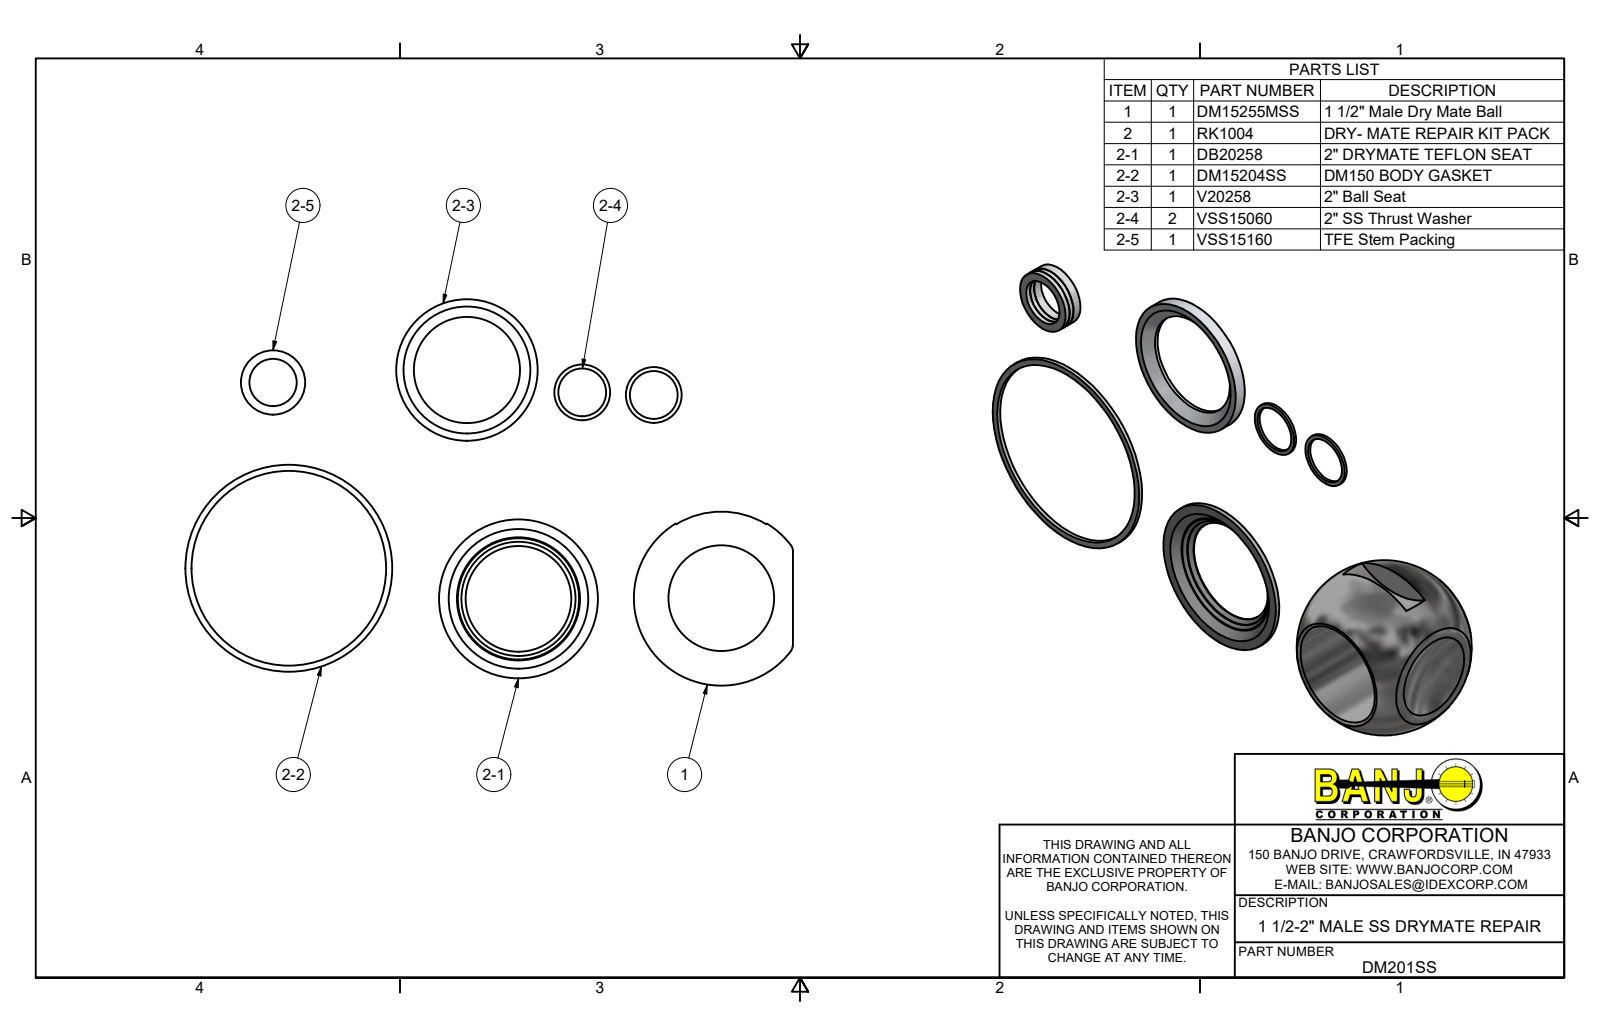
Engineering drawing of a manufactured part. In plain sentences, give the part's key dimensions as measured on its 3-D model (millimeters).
The part is named "DM201SS; RK1004; DB20258; DM15204SS (+7 more)". Its 3-D file was written by "Autodesk Inventor 2019 (AUTOMOTIVE_DESIGN)". It is 9 solids with 67 faces: 22 planar, 19 cylindrical and 26 other. Overall it measures 218.6 by 138.9 by 48.5 millimeters. Its volume is 68 370 cubic millimeters and its surface area 27 350 square millimeters. Round holes: 3 of diameter 38.1, 2 of diameter 17.2, 1 of diameter 17, 1 of diameter 41, 1 of diameter 70. Round bosses or shafts: 2 of diameter 20.1, 1 of diameter 74.5, 1 of diameter 57.2, 1 of diameter 50.8, 1 of diameter 23.2. Partial cylindrical surfaces (rounded edges, fillets, slot ends): 1 of radius 30. The main face-to-face distances are 6, 1.5, 4.4, 1.3, 4.6, 3.1, 4.2, 2.7, 0.5, 1.8. The hole center spacings are 25.8, 42.3, 67, 67.8, 70, 72.9, 77, 77.7.
